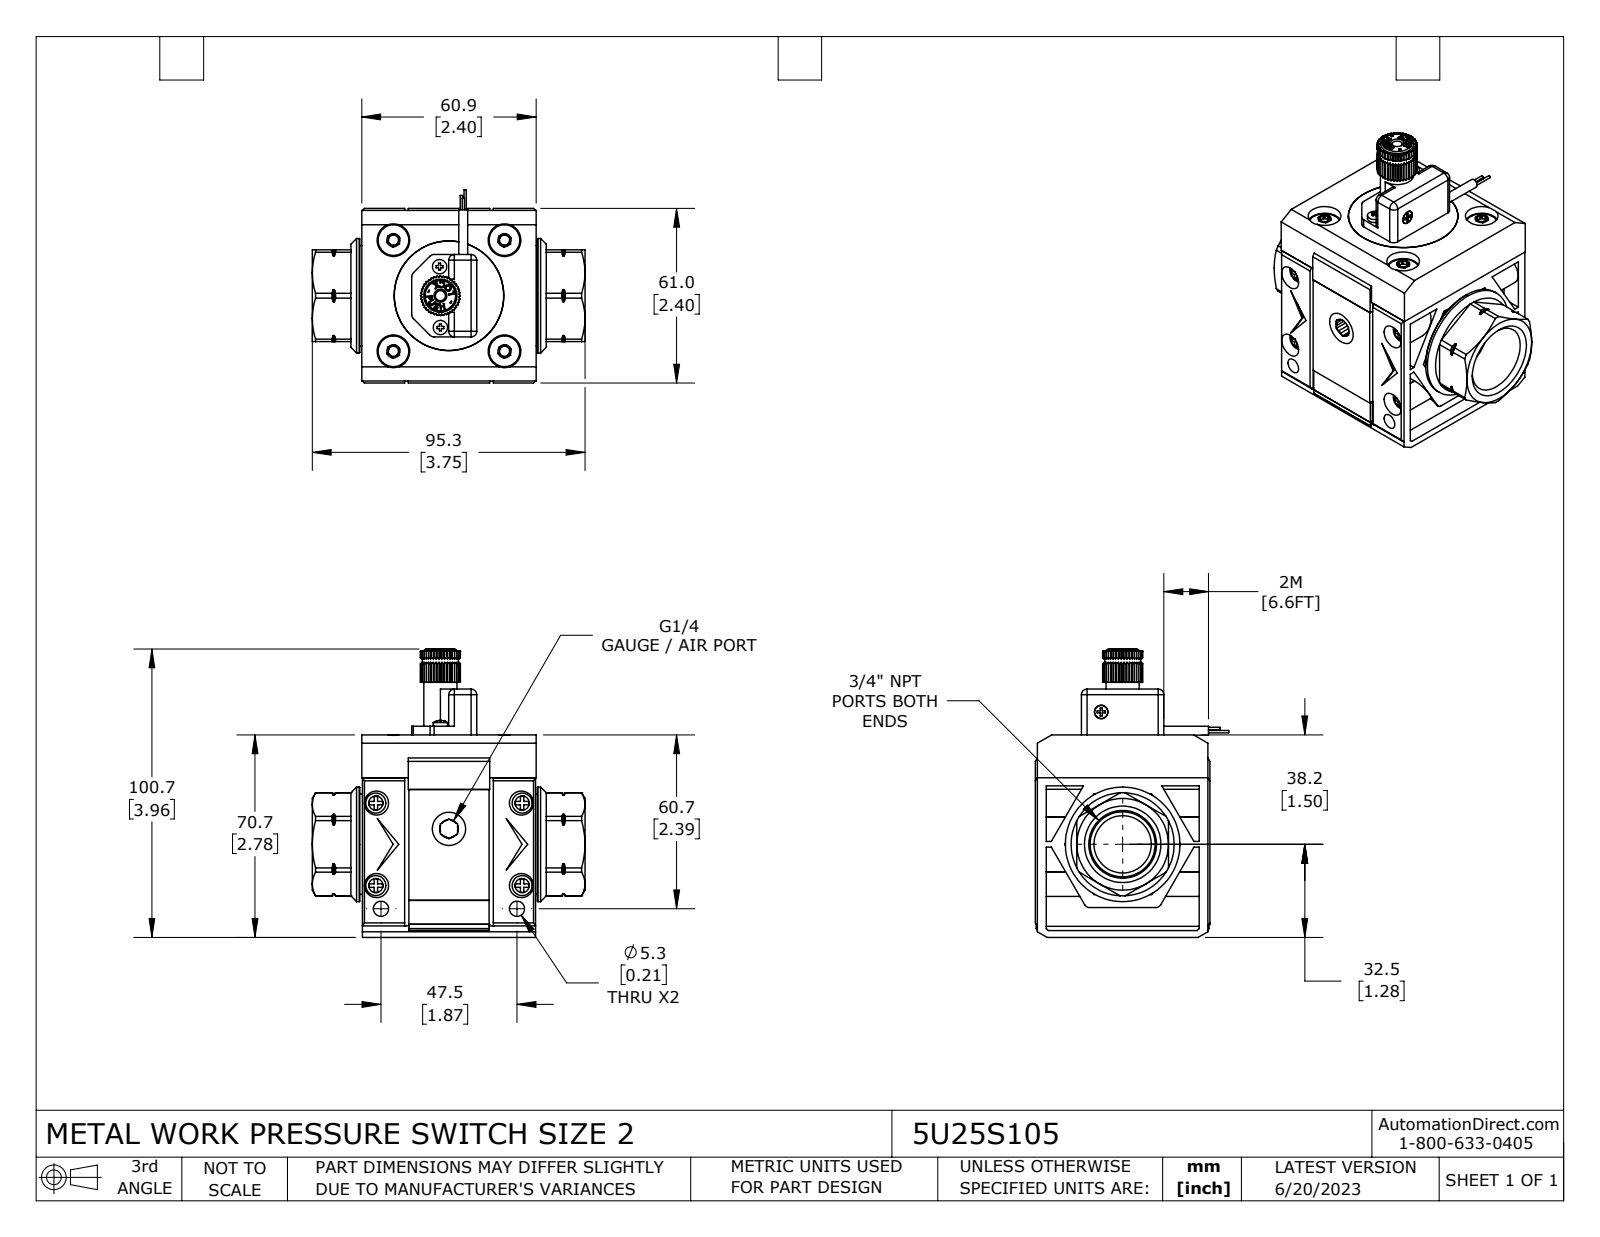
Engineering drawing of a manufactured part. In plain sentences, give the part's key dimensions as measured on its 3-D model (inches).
The part is named "5U25S105". Its 3-D file was written by "SolidWorks 2021 (CONFIG_CONTROL_DESIGN)". It is 13 solids with 1345 faces: 694 planar, 391 cylindrical and 260 other. Overall it measures 3.965 by 3.75 by 2.657 inches. Its volume is 13.61 cubic inches and its surface area 120.4 square inches. Round holes: 4 of diameter 0.128, 4 of diameter 0.165, 4 of diameter 0.331, 4 of diameter 0.449, 2 of diameter 0.209, 1 of diameter 0.071, 1 of diameter 0.457, 1 of diameter 0.787, 1 of diameter 1.25, 1 of diameter 1.508. Round bosses or shafts: 4 of diameter 0.276, 4 of diameter 0.189, 4 of diameter 0.15, 3 of diameter 0.031, 2 of diameter 0.197, 1 of diameter 1.575, 1 of diameter 1.504, 1 of diameter 1.378. Partial cylindrical surfaces (rounded edges, fillets, slot ends): 28 of radius 0.011, 14 of radius 0.079, 4 of radius 0.069, 4 of radius 0.191, 2 of radius 0.242, 1 of radius 0.008, 1 of radius 0.009, 1 of radius 0.009. The main face-to-face distances are 2.39, 0.094, 2.193, 2.098, 0.028, 2.402, 0.299, 1.799, 2.783, 2.689. The hole center spacings are 1.08, 1.528, 0.325, 1.057, 1.134, 1.265, 1.443, 1.454.
